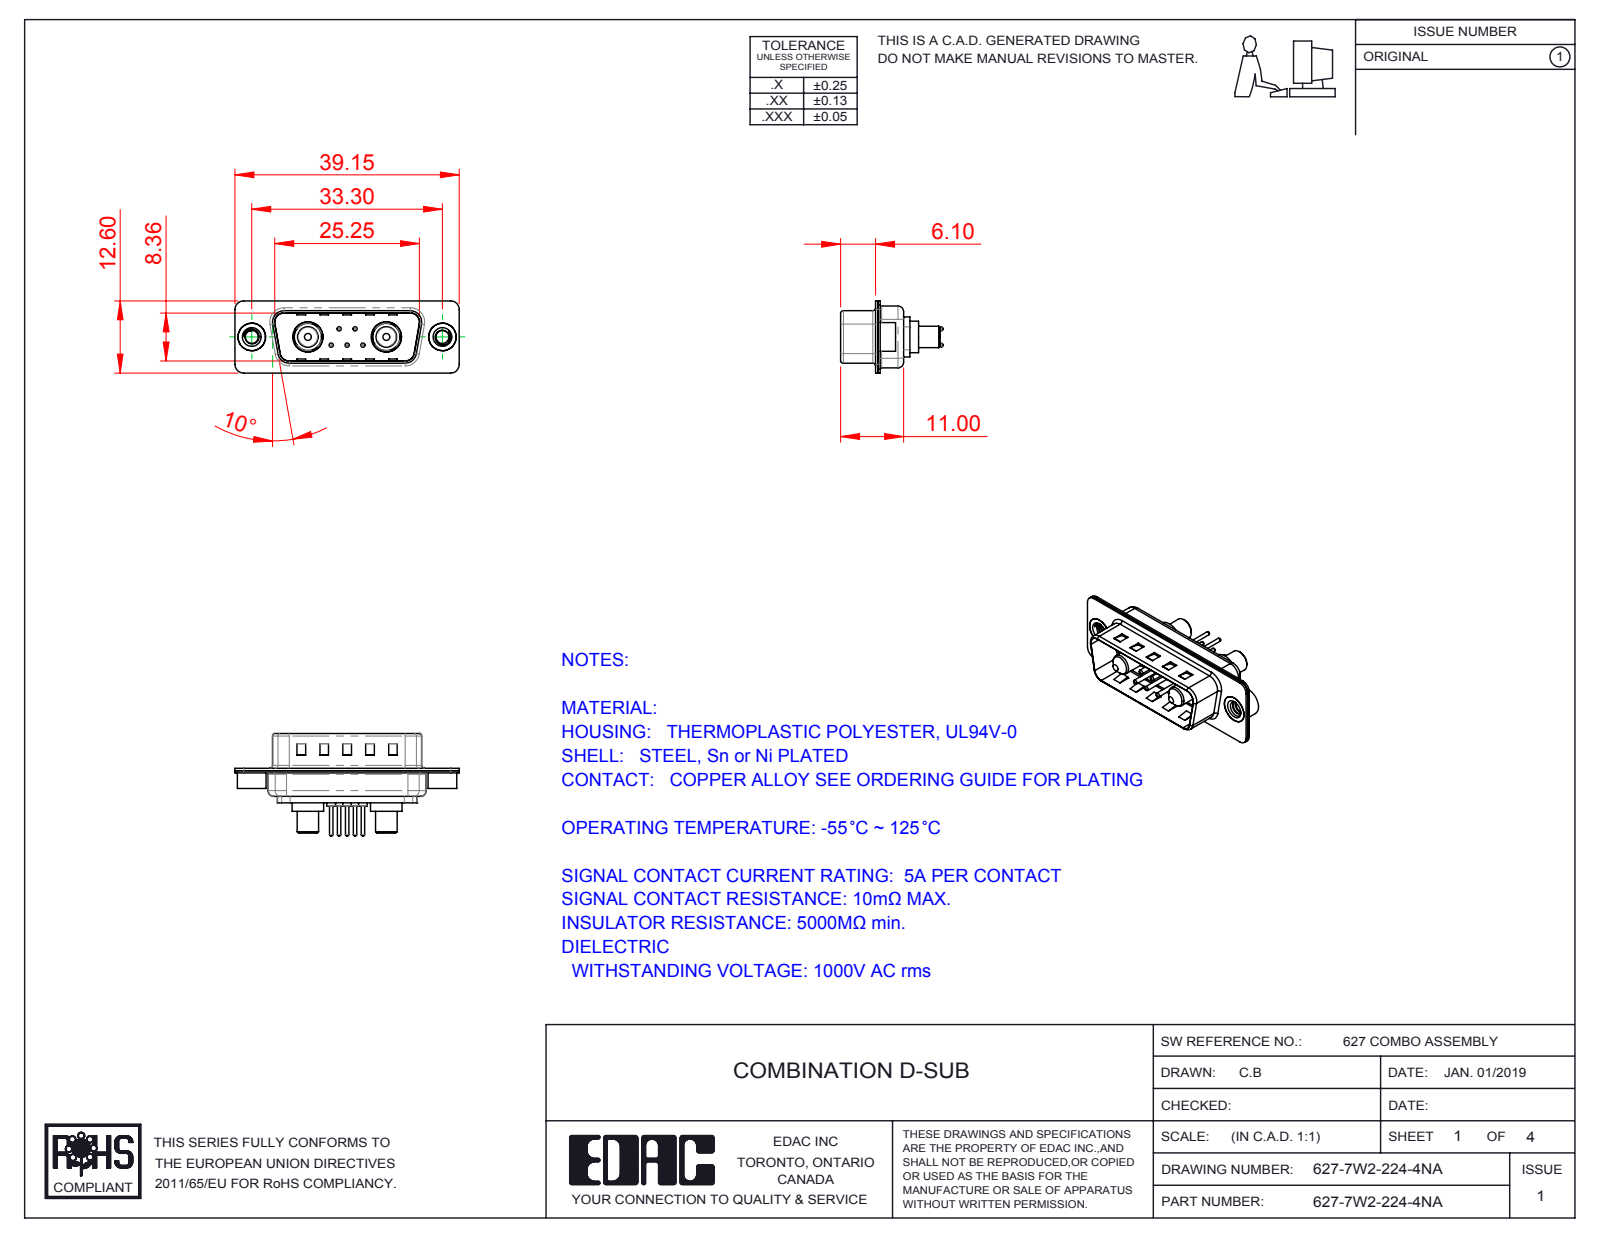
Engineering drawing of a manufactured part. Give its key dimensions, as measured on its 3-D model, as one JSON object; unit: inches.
{"part_name": "Power Pin_40A S; 627Combo Housing_7W2; 627Combo Shell Front_15 Contacts; 627Combo Contact Row 2_24 (+5 more)", "step_written_by": "SolidWorks 2016 (CONFIG_CONTROL_DESIGN)", "units": "inches", "bodies": {"solids": 14, "faces": 604, "planar": 194, "cylindrical": 242, "other": 168}, "overall_size": [1.541, 0.705, 0.496], "volume_in3": 0.123, "surface_area_in2": 7.389, "round_holes": [[0.03, 5], [0.063, 5], [0.079, 5], [0.089, 2], [0.157, 2], [0.189, 2], [0.191, 2], [0.209, 2]], "round_bosses_or_shafts": [[0.059, 5], [0.024, 5], [0.217, 2], [0.205, 2], [0.197, 2], [0.193, 2], [0.187, 2], [0.148, 2]], "partial_cylinders_radius": [[0.059, 20], [0.079, 12], [0.02, 8], [0.063, 8], [0.01, 4], [0.024, 4], [0.026, 4], [0.035, 4]], "face_to_face_distances": [0.016, 0.032, 0.377, 0.031, 0.345, 0.22, 0.059, 0.055, 0.205, 0.236], "hole_center_spacings": [0.124, 0.109, 0.386, 0.925, 0.17, 0.17, 0.198, 0.198]}
